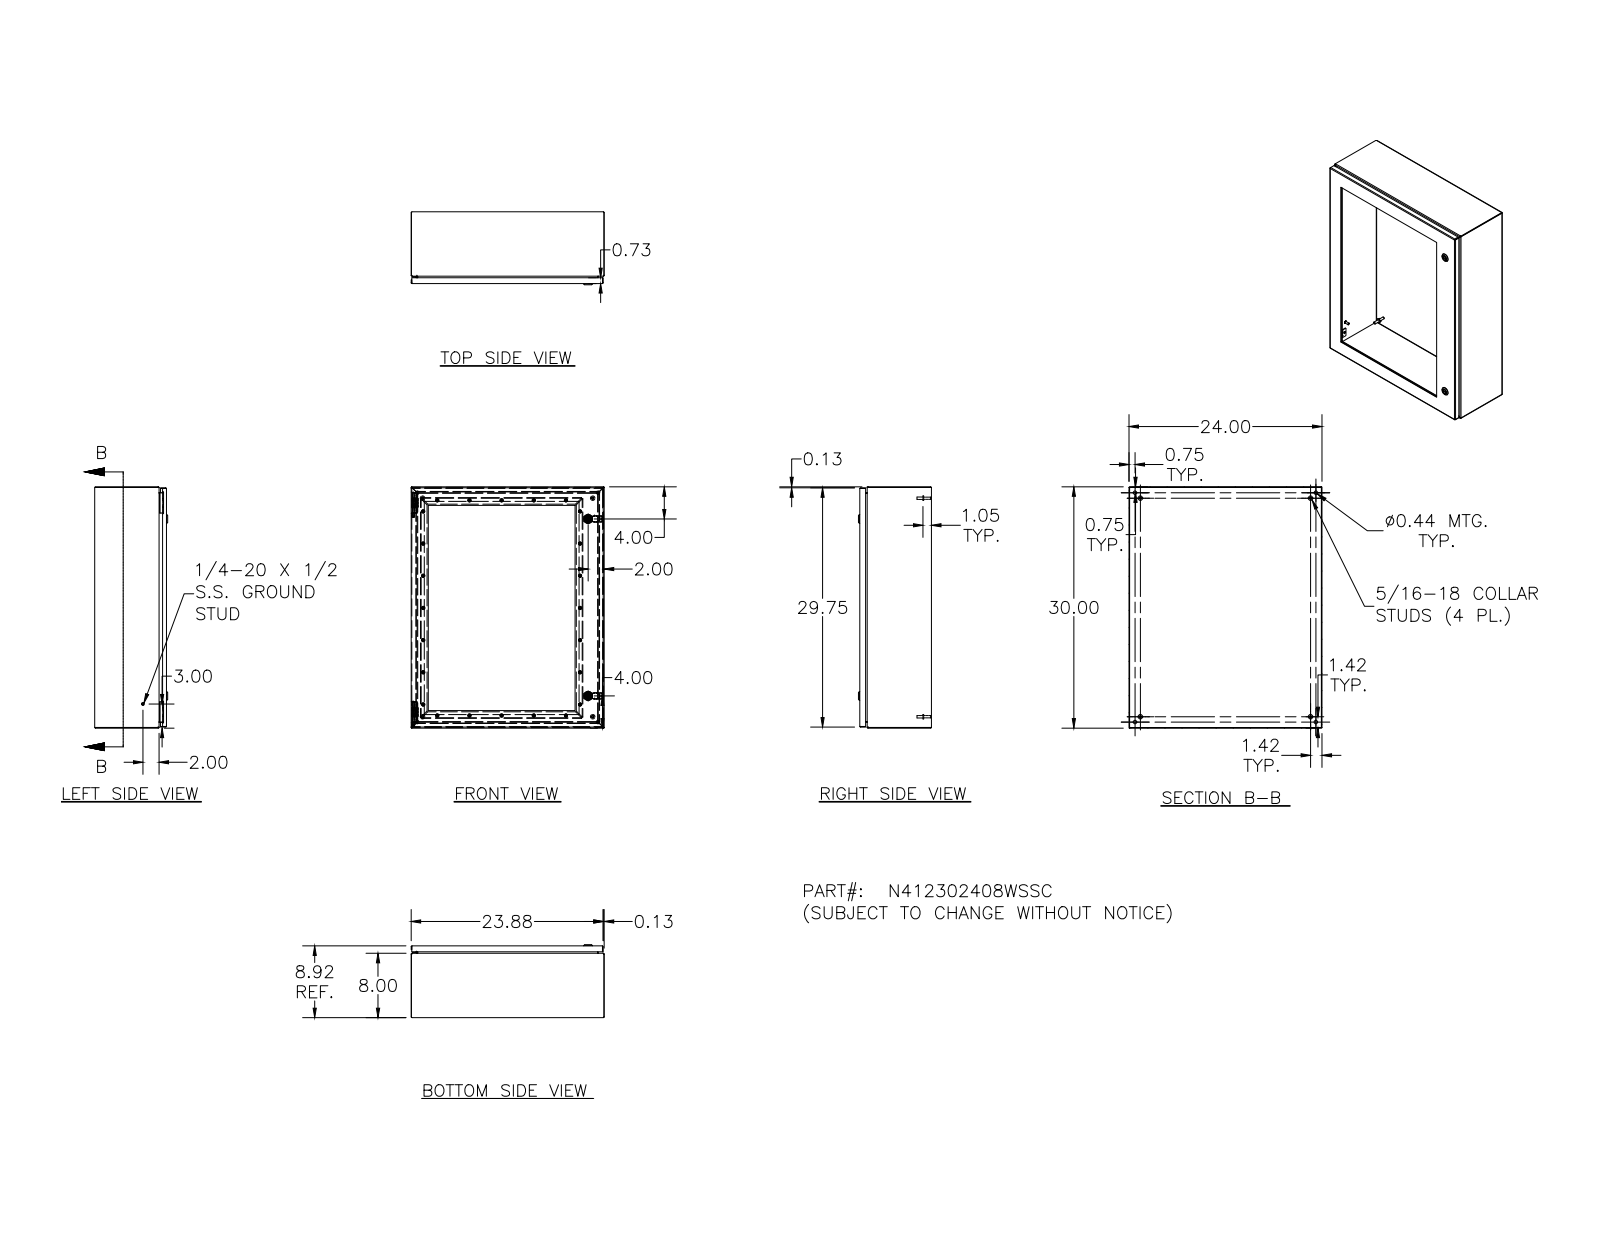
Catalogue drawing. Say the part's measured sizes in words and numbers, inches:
The part is named "N412302408WSSC; N412302408WSSCBKP; N4123024WSSCLID; HFW328176 (+8 more)". Its 3-D file was written by "Autodesk Inventor 2011 (AUTOMOTIVE_DESIGN)". It is 94 solids with 2494 faces: 1017 planar, 688 cylindrical and 789 other. Overall it measures 30 by 24 by 9.075 inches. Its volume is 287.8 cubic inches and its surface area 5 417 square inches. Round holes: 26 of diameter 0.156, 24 of diameter 0.281, 4 of diameter 0.093, 4 of diameter 0.152, 4 of diameter 0.167, 4 of diameter 0.172, 4 of diameter 0.188, 4 of diameter 0.437, 2 of diameter 0.197, 2 of diameter 0.315, 2 of diameter 0.394, 2 of diameter 0.402. Round bosses or shafts: 24 of diameter 0.19, 23 of diameter 0.253, 10 of diameter 0.25, 4 of diameter 0.563, 4 of diameter 0.36, 4 of diameter 0.32, 4 of diameter 0.3, 4 of diameter 0.275. Partial cylindrical surfaces (rounded edges, fillets, slot ends): 34 of radius 0.031, 26 of radius 0.05, 24 of radius 0.105, 18 of radius 0.016, 16 of radius 0.125, 15 of radius 0.02, 8 of radius 0.032, 8 of radius 0.157. The main face-to-face distances are 0.074, 8.843, 8.769, 0.25, 8.593, 8.519, 23.926, 29.926, 8.917, 0.324. The hole center spacings are 4, 8, 12, 27.047, 26, 27.92, 16, 26.75.
